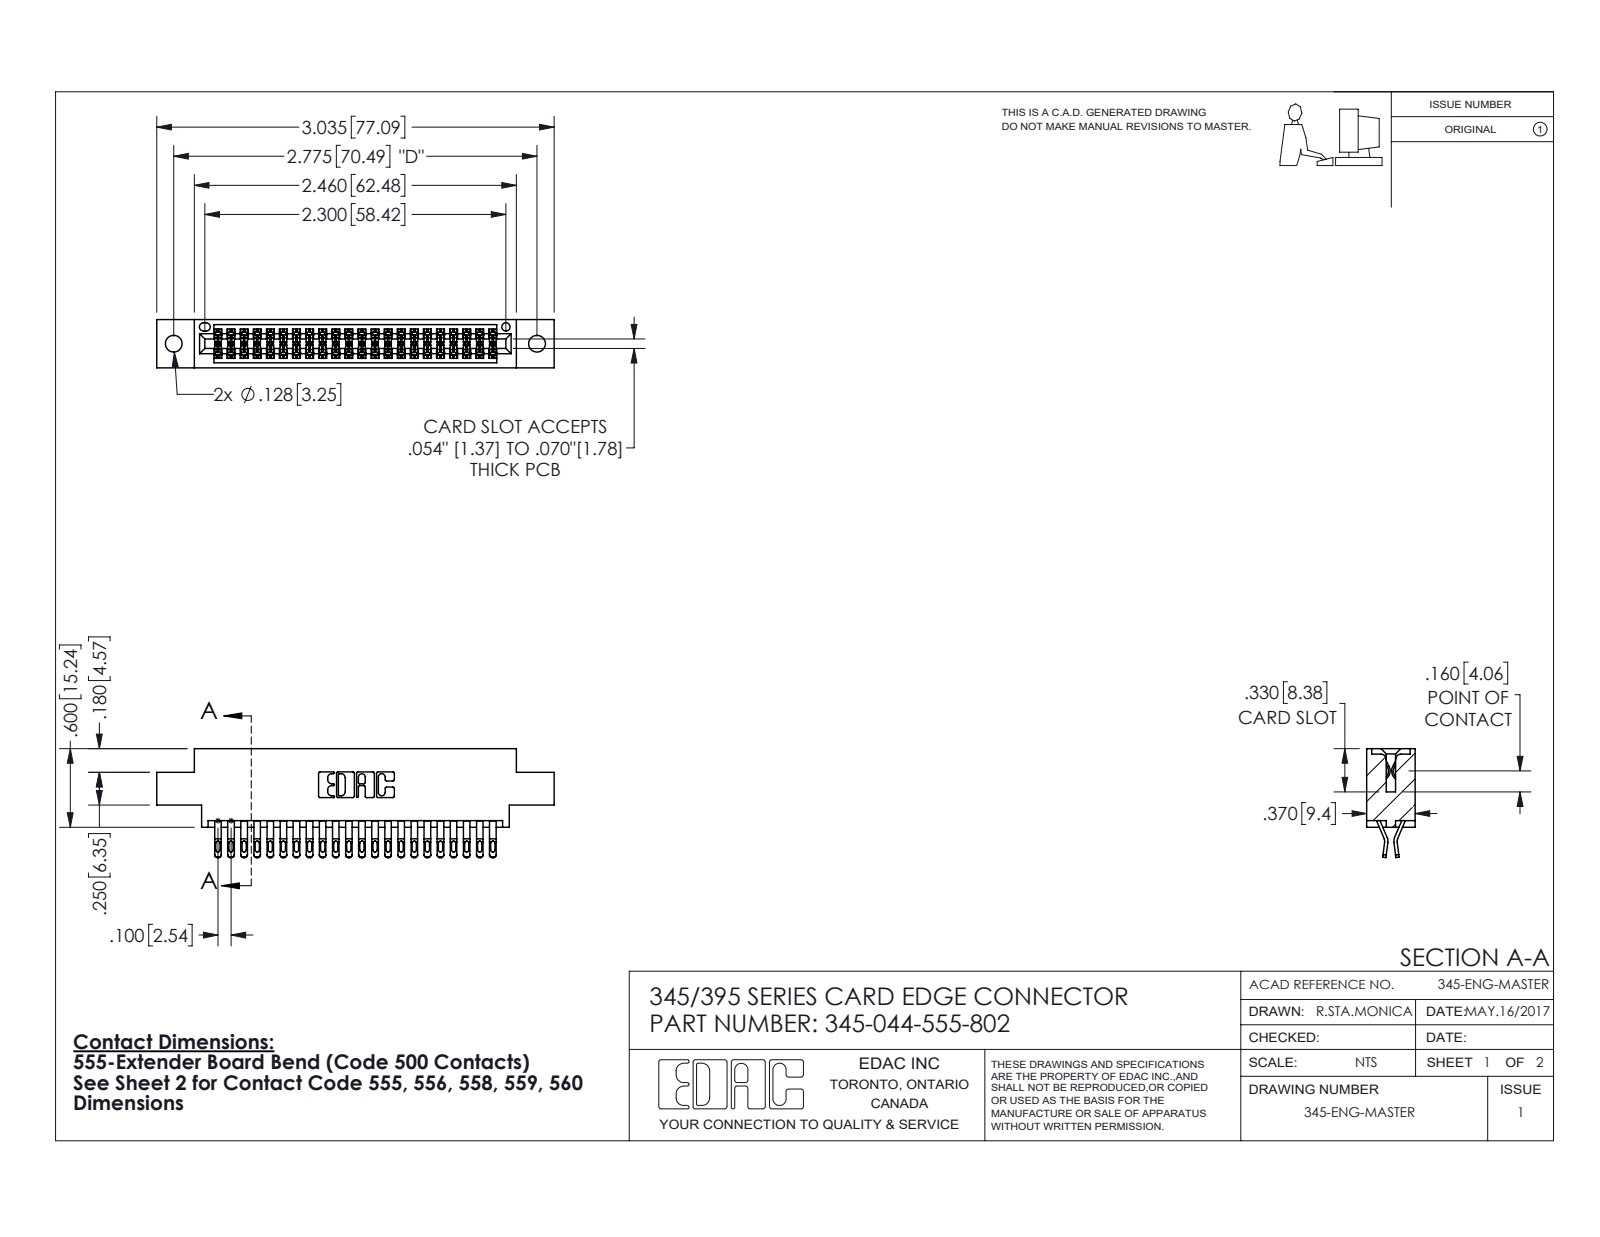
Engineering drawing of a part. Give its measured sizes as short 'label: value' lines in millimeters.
name: 345-292-001_555 Tail; 345-044-555-802; 345 Part_0.170 Offset - 0.128 Dia
written by: SolidWorks 2016 (CONFIG_CONTROL_DESIGN)
unit: mm
bodies: 45 solids, 2594 faces (1448 planar, 1146 cylindrical, 0 other)
size: 77.1 × 21.1 × 9.4
volume: 7 280 mm³; area: 10 690 mm²
holes: 2× ⌀3.3, 1× ⌀1.6
rounds: 110× R0.4, 88× R0.5, 66× R0.2, 22× R0.3, 6× R0.2, 6× R0.8, 3× R0.7, 2× R0.3
face distances: 7.6, 1.8, 9.4, 0.6, 5.1, 2.5, 6.9, 5.7, 4.4, 3.8
hole spacings: 6.9, 64.5, 70.5
